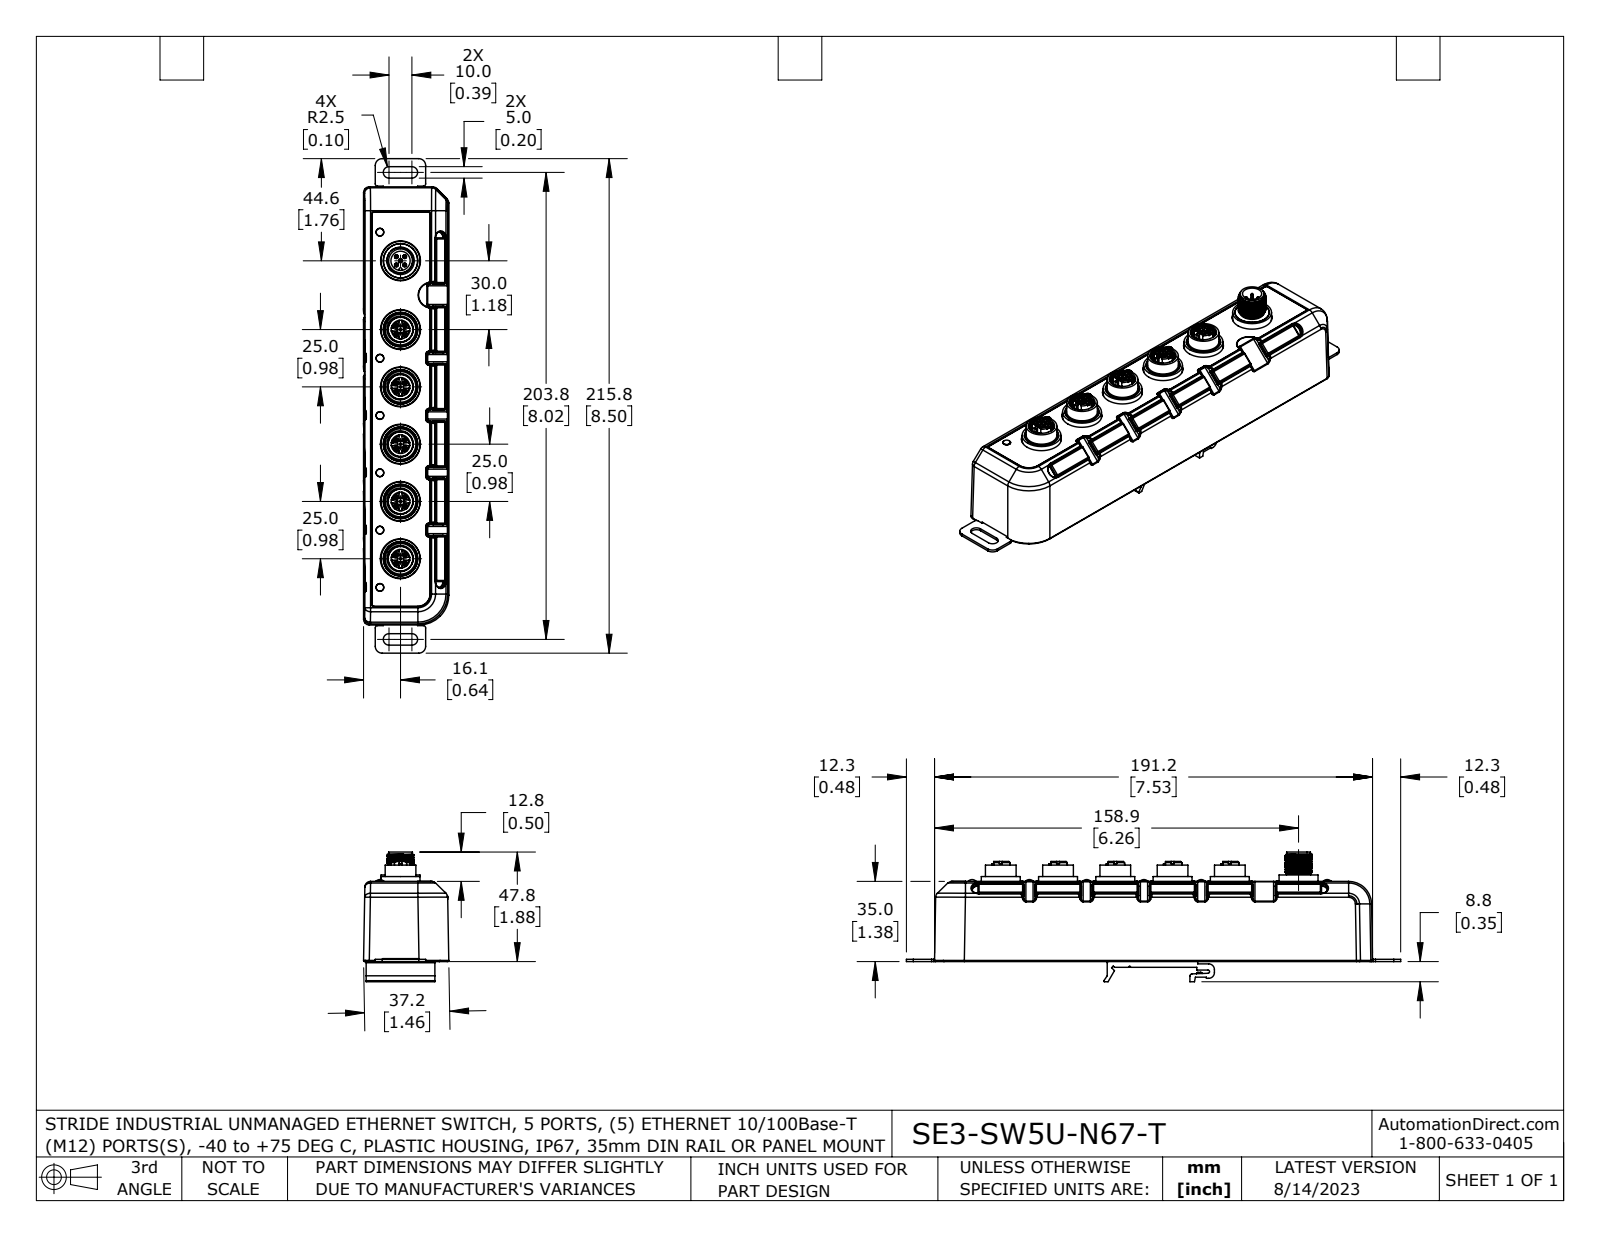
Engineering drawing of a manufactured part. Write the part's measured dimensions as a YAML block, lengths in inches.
part_name: "LEONTON_ET2-0500-M12-67_3D fxtrd1"
step_written_by: "SolidWorks 2021 (AUTOMOTIVE_DESIGN)"
units: inches
bodies: {solids: 59, faces: 3705, planar: 1116, cylindrical: 1655, other: 934}
overall_size: [8.495, 2.228, 1.465]
volume: 6.827
surface_area: 136.1
round_holes:
  - {diameter: 0.043, count: 20}
  - {diameter: 0.065, count: 20}
  - {diameter: 0.077, count: 20}
  - {diameter: 0.118, count: 11}
  - {diameter: 0.134, count: 6}
  - {diameter: 0.197, count: 6}
  - {diameter: 0.512, count: 6}
  - {diameter: 0.591, count: 6}
  - {diameter: 0.669, count: 6}
  - {diameter: 0.685, count: 6}
  - {diameter: 0.039, count: 5}
  - {diameter: 0.343, count: 5}
round_bosses_or_shafts:
  - {diameter: 0.063, count: 25}
  - {diameter: 0.031, count: 25}
  - {diameter: 0.748, count: 6}
  - {diameter: 0.516, count: 6}
  - {diameter: 0.13, count: 6}
  - {diameter: 0.112, count: 6}
  - {diameter: 0.528, count: 5}
  - {diameter: 0.492, count: 5}
partial_cylinders:
  - {radius: 0.02, count: 242}
  - {radius: 0.004, count: 96}
  - {radius: 0.039, count: 88}
  - {radius: 0.012, count: 33}
  - {radius: 0.005, count: 24}
  - {radius: 0.098, count: 18}
  - {radius: 0.008, count: 15}
  - {radius: 0.016, count: 13}
face_to_face_distances: [1.358, 1.319, 0.039, 0.317, 0.138, 0.12, 1.378, 0.02, 1.339, 1.181]
hole_center_spacings: [0.098, 0.139, 0.984, 0.917, 0.994, 1.056, 1.969, 1.9]
